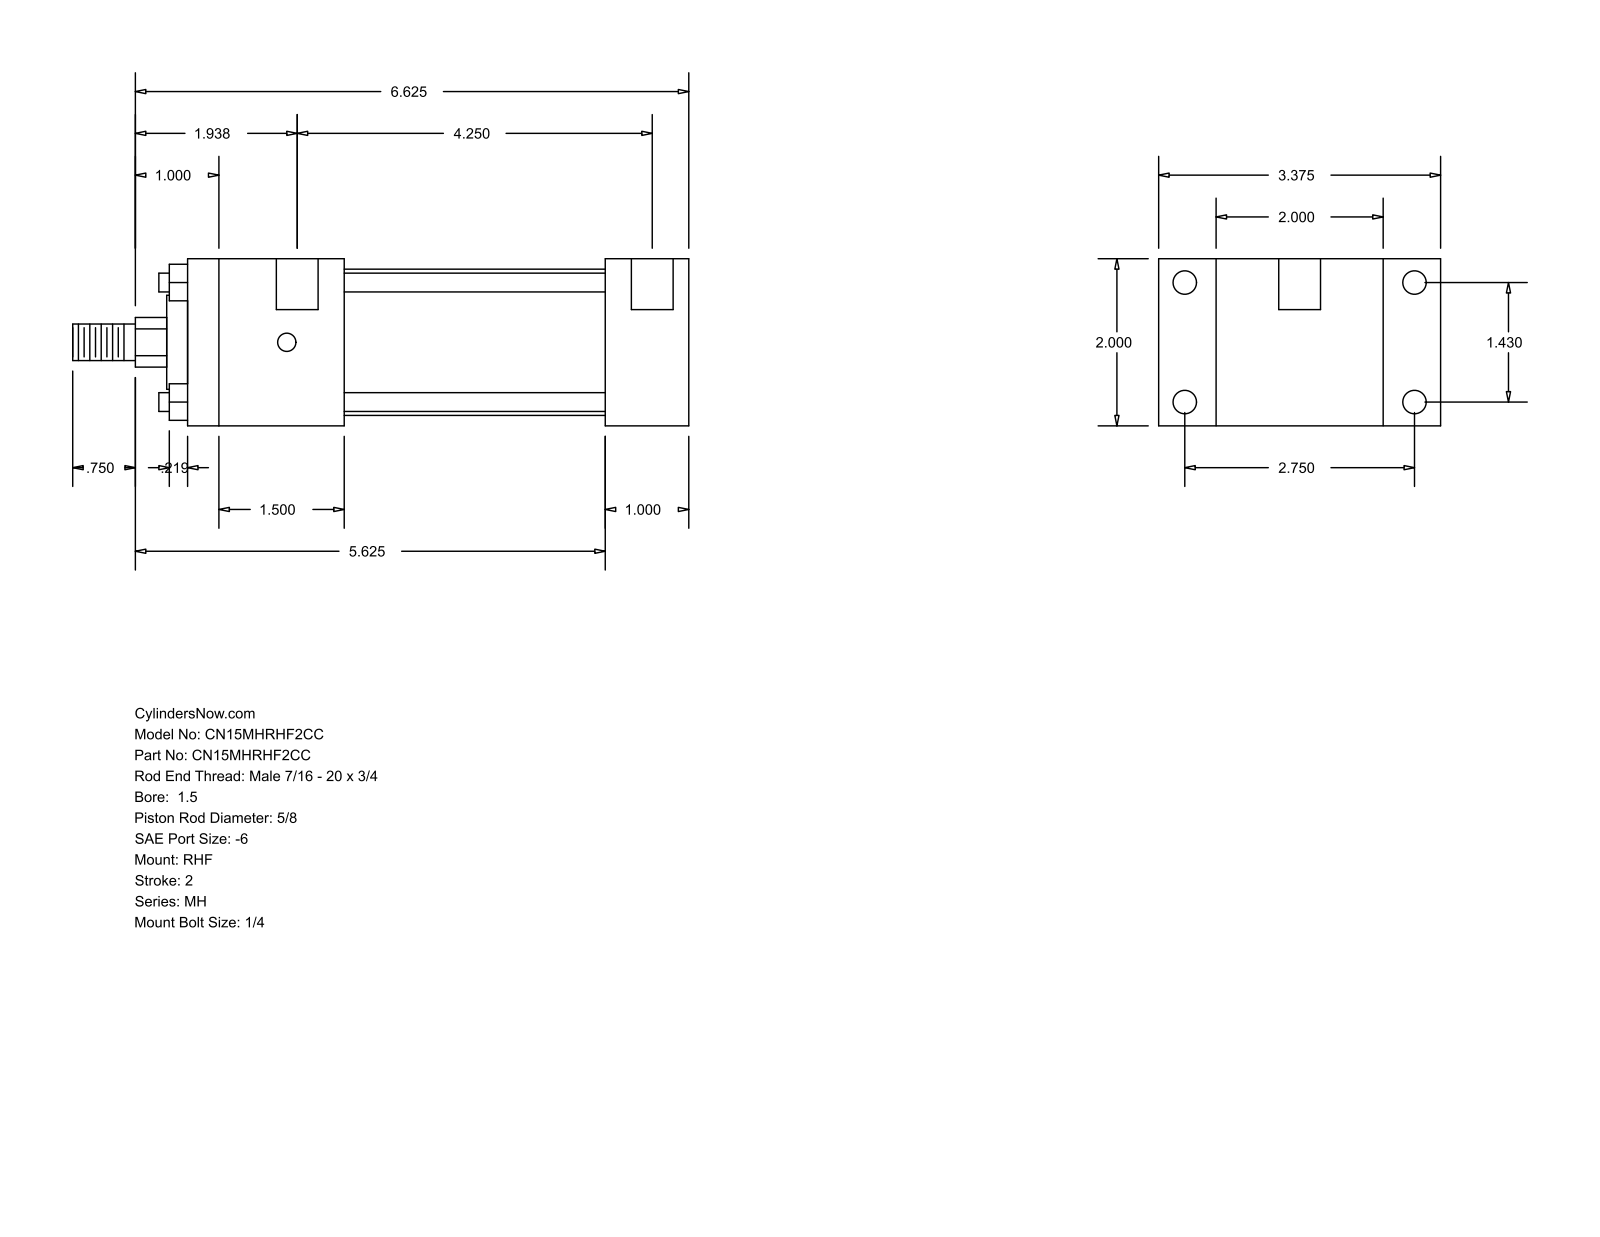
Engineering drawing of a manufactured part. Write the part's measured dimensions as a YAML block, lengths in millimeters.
part_name: "MH_RHF__0150_0.625"
step_written_by: "GSSL Pune (CONFIG_CONTROL_DESIGN)"
units: millimeters
bodies: {solids: 0, faces: 88, planar: 60, cylindrical: 28, other: 0}
overall_size: [187.32, 85.72, 50.8]
round_holes:
  - {diameter: 5.56, count: 4}
  - {diameter: 7.14, count: 4}
  - {diameter: 12.7, count: 2}
round_bosses_or_shafts:
  - {diameter: 5.71, count: 4}
  - {diameter: 44.45, count: 1}
  - {diameter: 28.57, count: 1}
  - {diameter: 15.88, count: 1}
  - {diameter: 11.11, count: 1}
partial_cylinders:
  - {radius: 7.54, count: 1}
face_to_face_distances: [50.8, 25.4, 17.46, 68.26, 127, 152.4, 85.72, 47.62, 79.38, 104.78]
hole_center_spacings: [36.32, 69.84, 78.72, 111.12, 3.17, 107.95]
